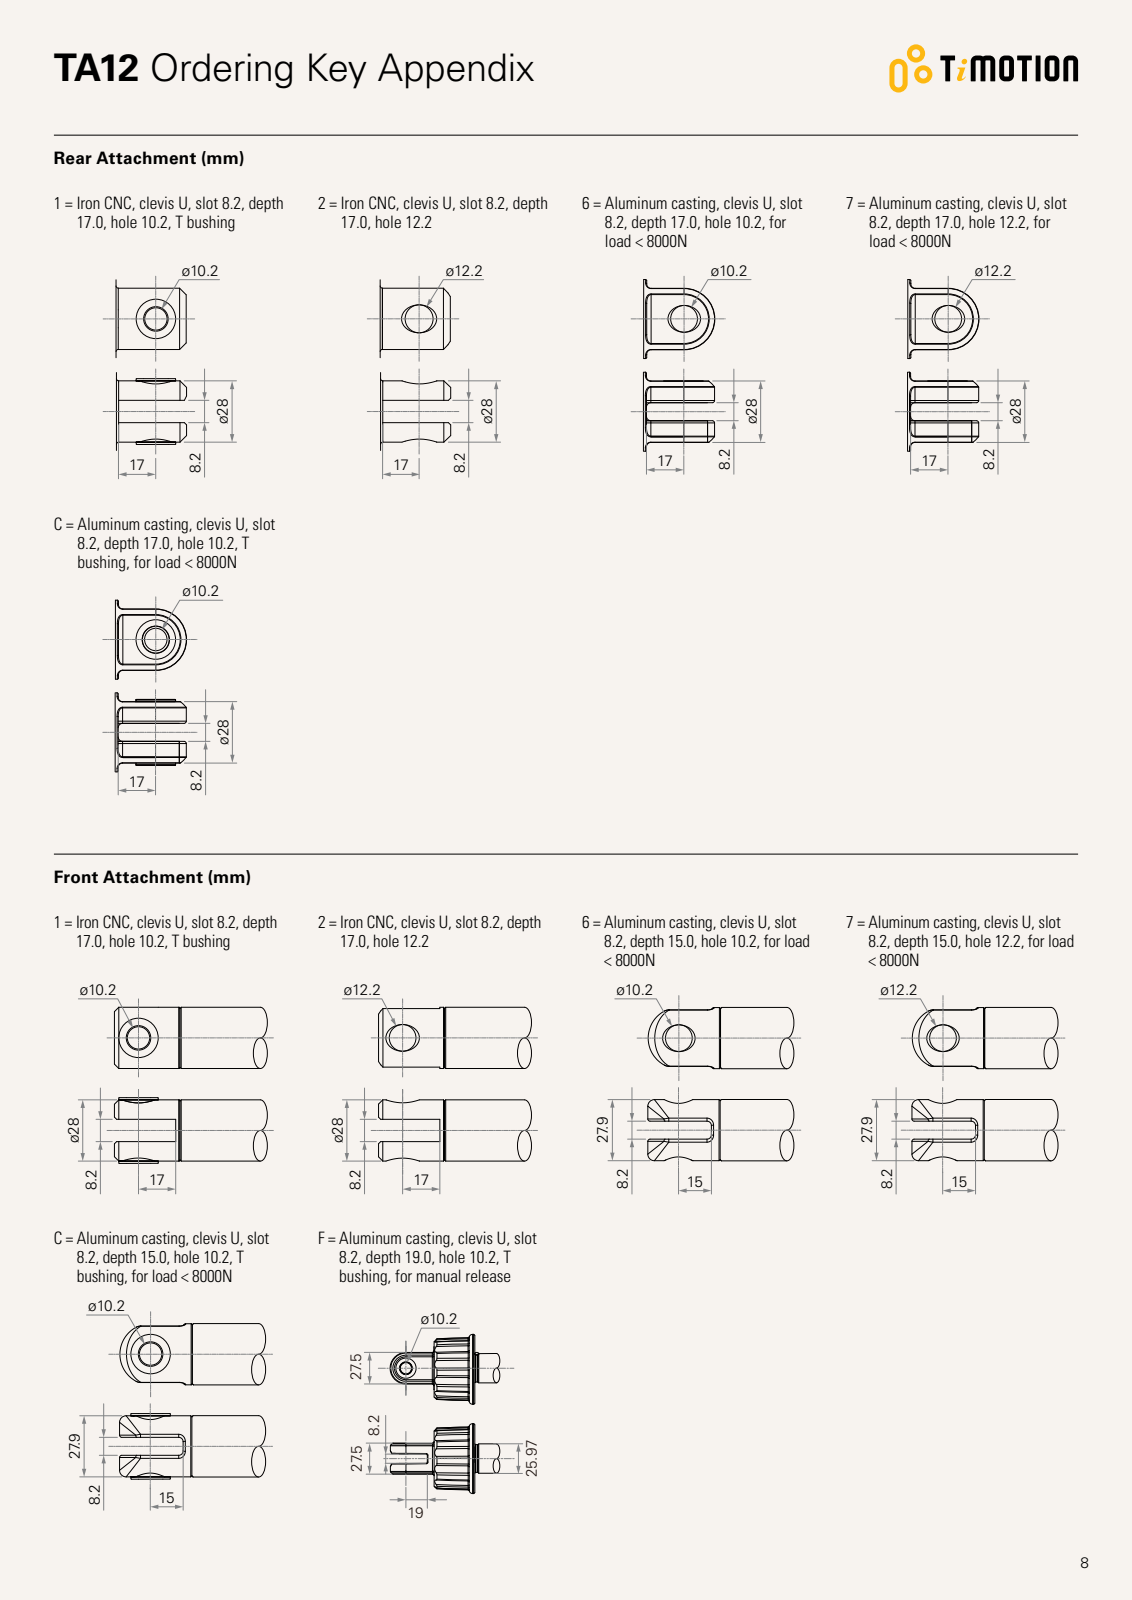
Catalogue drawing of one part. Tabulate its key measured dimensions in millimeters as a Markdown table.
| quantity | value |
| --- | --- |
| part name | TA12 |
| STEP written by | SolidWorks 2010 (CONFIG_CONTROL_DESIGN) |
| units | millimeters |
| bodies | 1 solid, 203 faces (27 planar, 26 cylindrical, 150 other) |
| overall size | 495 × 196.88 × 99.52 |
| volume | 2 141 000 mm³ |
| surface area | 131 966 mm² |
| round holes (diameter × count) | 10.2 × 2 |
| round bosses / shafts (diameter × count) | 6 × 3, 28 × 1 |
| partial cylindrical surfaces (radius × count) | 5 × 4, 6 × 4 |
| main face-to-face distances | 8.2, 395.5, 28, 467, 420.5, 25, 239.7, 155.8, 180.8, 424.5 |
| hole center spacings | 470 |
